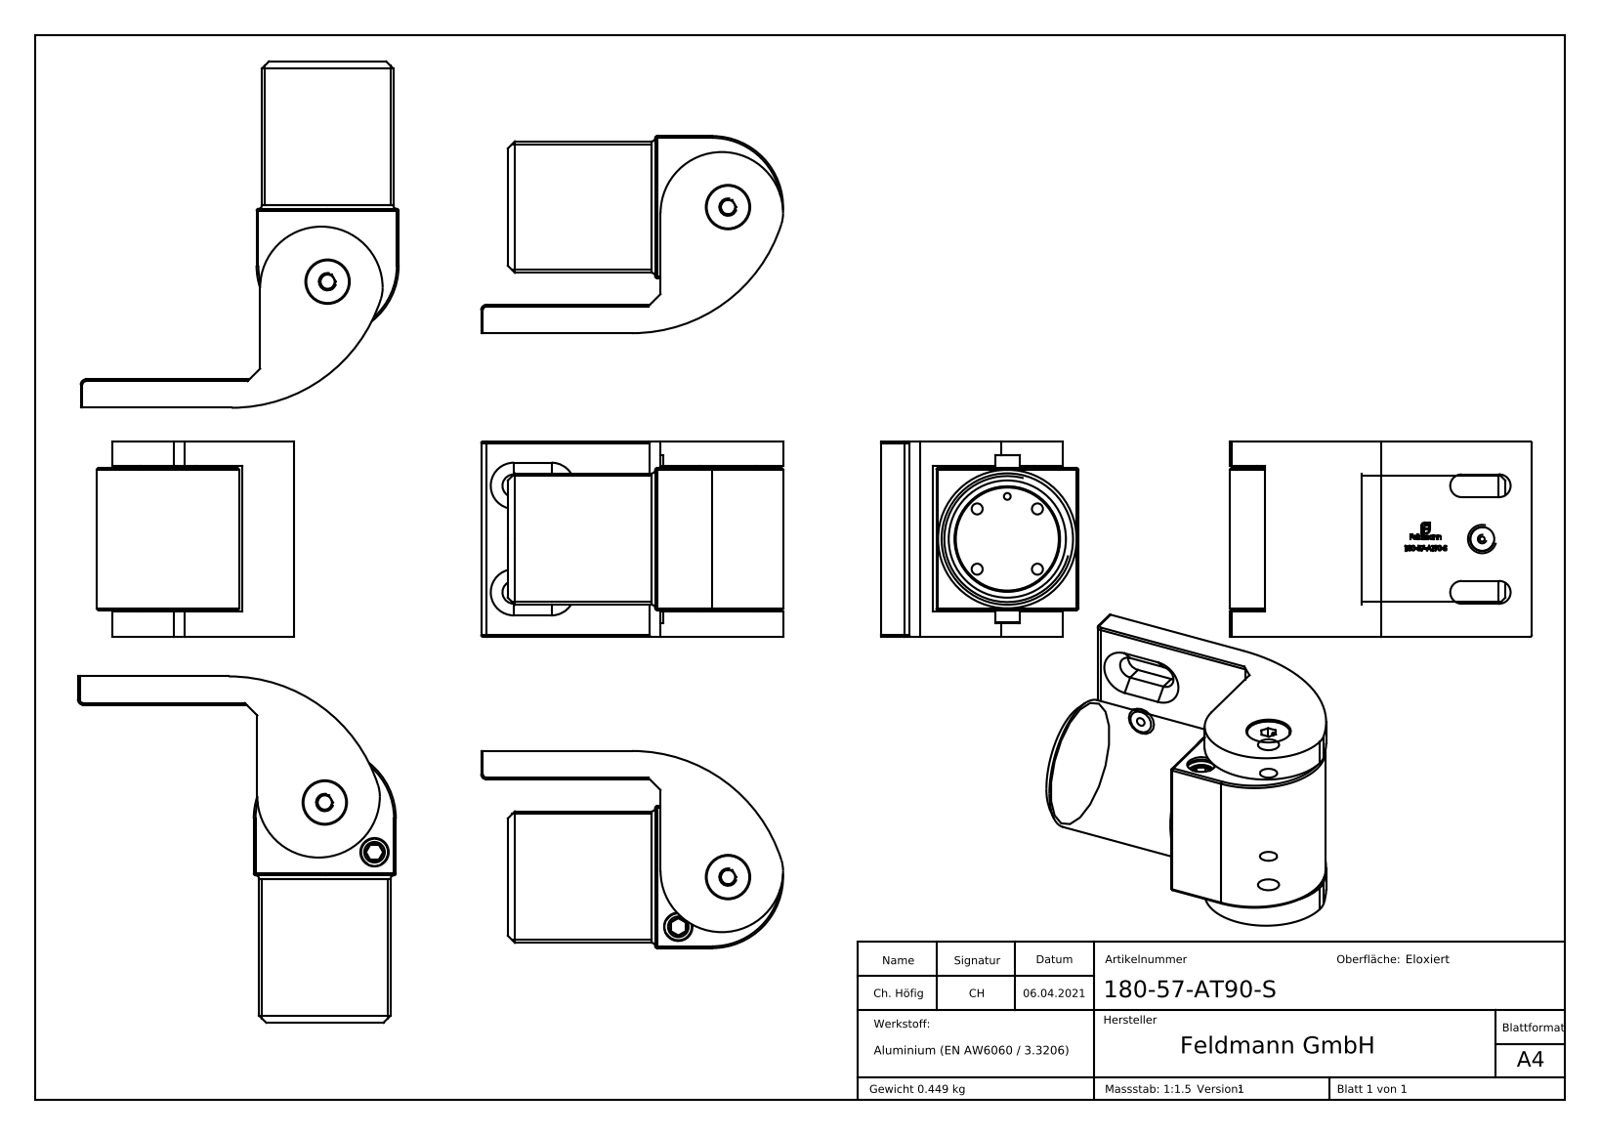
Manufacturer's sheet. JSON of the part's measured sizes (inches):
{"part_name": "DIN914_DIN 914 M8x8; Teil1_180-57-AT90-S Teil1; Teil2; 180-57-AT90-S (+5 more)", "step_written_by": "SolidWorks 2018 (CONFIG_CONTROL_DESIGN)", "units": "inches", "bodies": {"solids": 6, "faces": 575, "planar": 270, "cylindrical": 92, "other": 213}, "overall_size": [551.199, 236.215, 236.209], "volume_in3": 8.598, "surface_area_in2": 49.2, "round_holes": [[0.122, 4], [0.075, 1], [0.197, 1], [0.256, 1], [0.268, 1], [0.315, 1], [0.492, 1], [0.618, 1], [0.945, 1], [1.169, 1]], "round_bosses_or_shafts": [[1.457, 1], [1.161, 1], [1.024, 1], [0.929, 1], [0.61, 1], [0.472, 1], [0.315, 1], [0.307, 1]], "partial_cylinders_radius": [[0.02, 12], [0.126, 4], [0.059, 1], [0.394, 1], [0.679, 1], [0.787, 1], [1.737, 1]], "face_to_face_distances": [0.295, 1.87, 0.276, 0.315, 1.89, 2.165, 1.614, 0.02, 1.594, 1.575], "hole_center_spacings": [0.473, 0.669, 0.362, 0.873, 0.945, 0.472, 0.78]}
